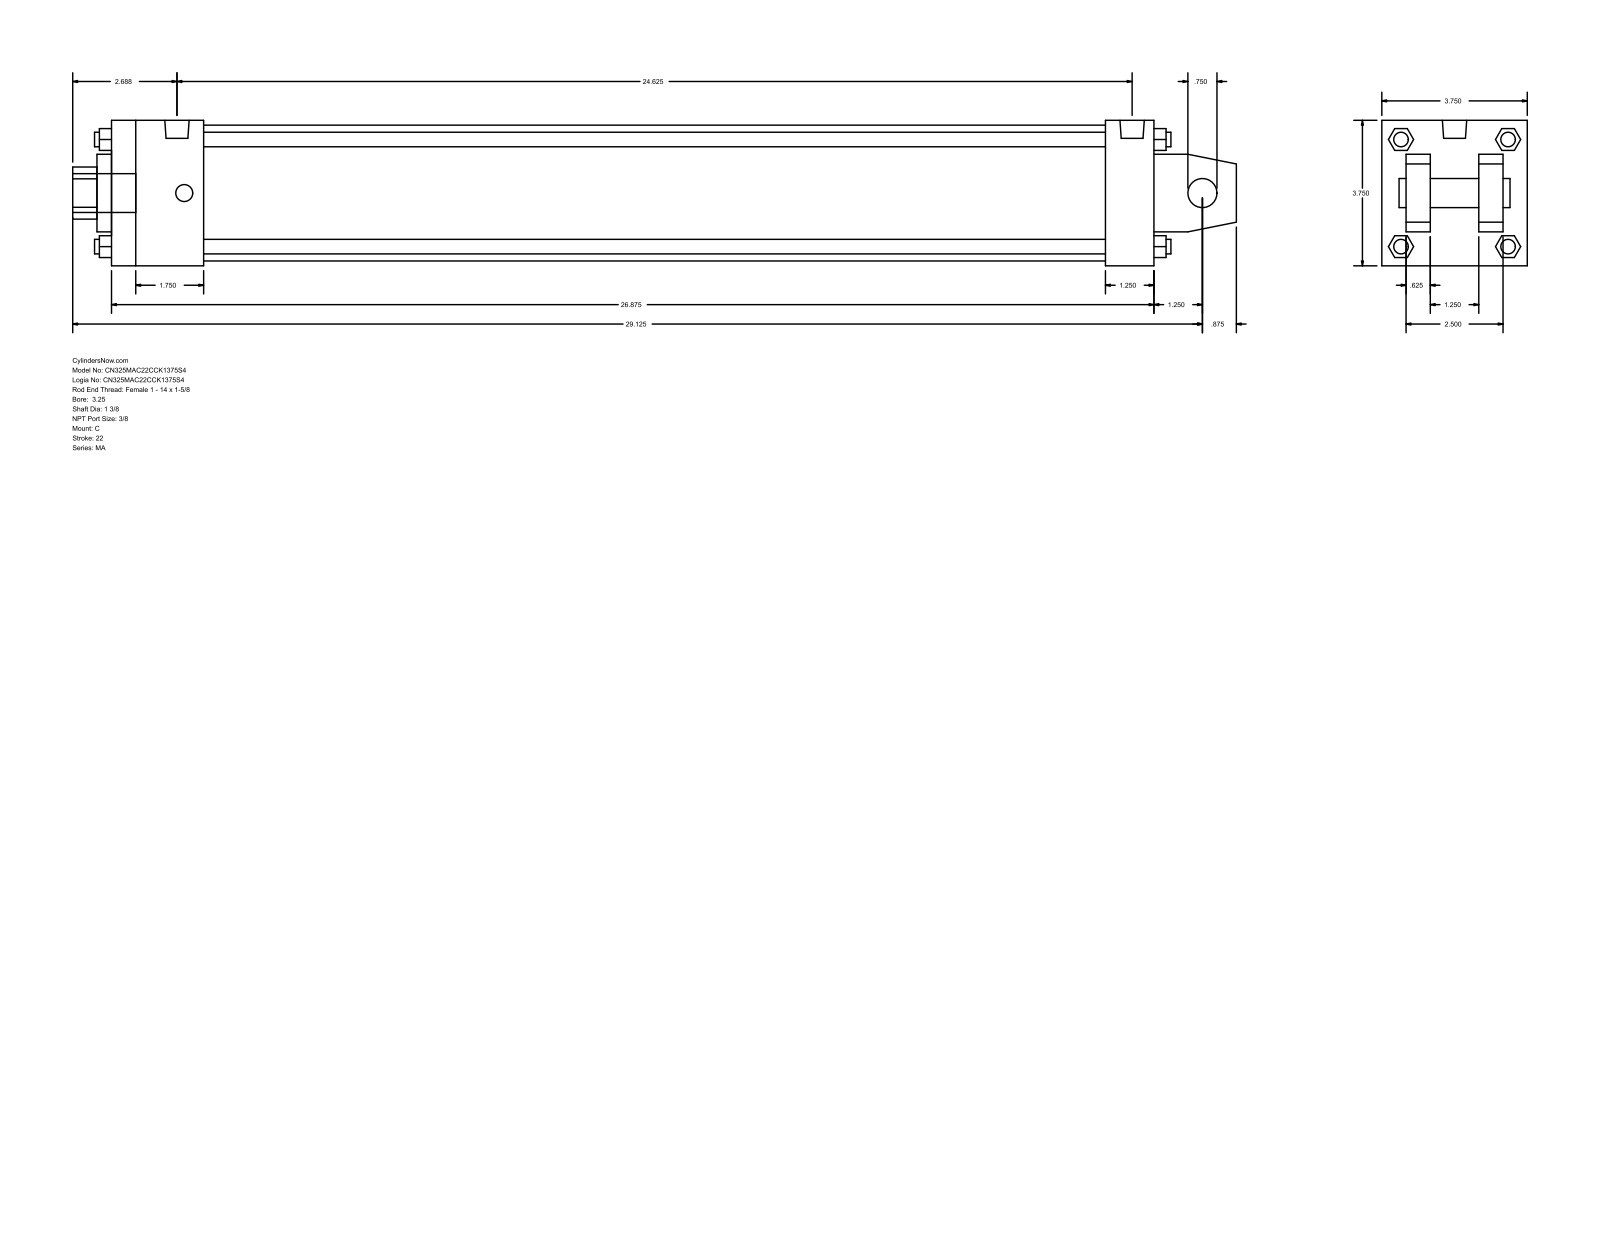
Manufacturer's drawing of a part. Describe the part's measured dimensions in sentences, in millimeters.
The part is named "MA_C__0325_1.375". Its 3-D file was written by "GSSL Pune (CONFIG_CONTROL_DESIGN)". It is 0 solids with 139 faces: 108 planar, 31 cylindrical and 0 other. Overall it measures 762 by 95.25 by 95.25 millimeters. Round holes: 1 of diameter 19.05, 1 of diameter 34.92, 1 of diameter 50.8, 1 of diameter 88.9. Round bosses or shafts: 4 of diameter 11.11, 4 of diameter 9.53, 2 of diameter 15.93, 1 of diameter 25.4. Partial cylindrical surfaces (rounded edges, fillets, slot ends): 1 of radius 17.06. The main face-to-face distances are 95.24, 15.87, 63.5, 682.62, 31.74, 79.37, 47.63, 650.87, 31.75, 60.32.
